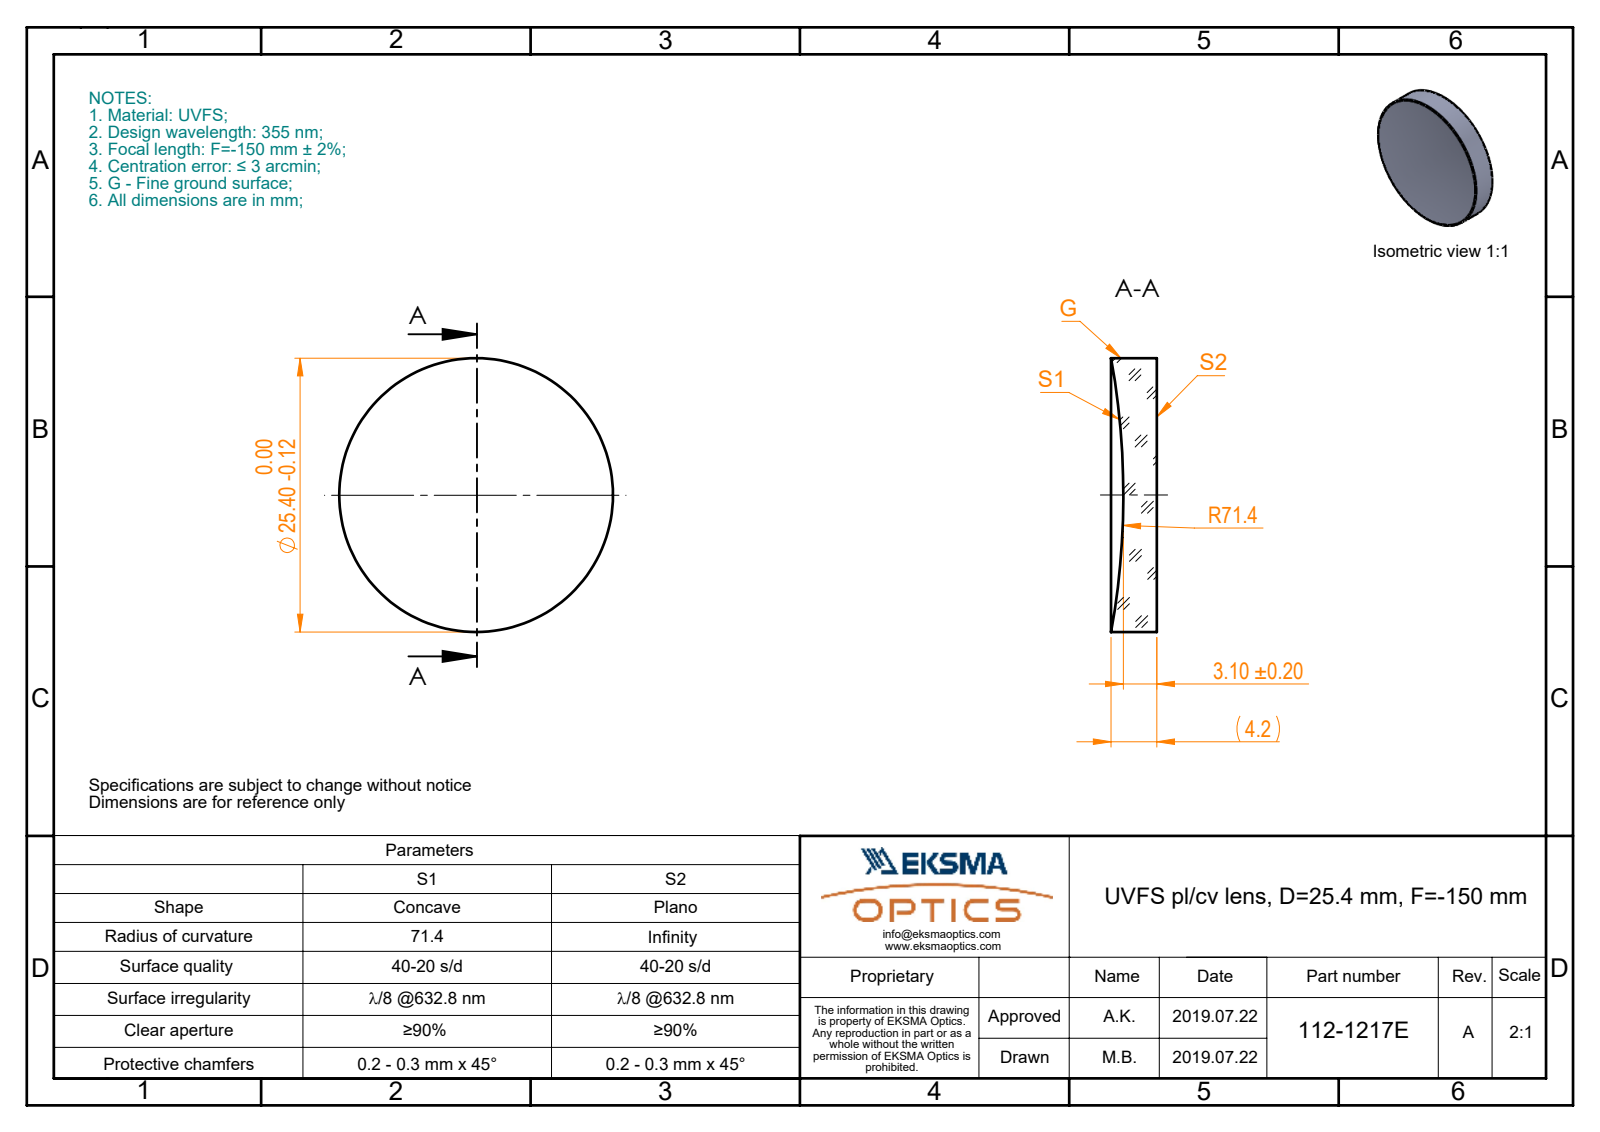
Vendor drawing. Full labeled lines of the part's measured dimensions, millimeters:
Part name (STEP PRODUCT): 112-1217E UVFS pl-cv 25.4 F-150
STEP written by: SolidWorks 2017 (CONFIG_CONTROL_DESIGN)
Units: millimetres
Bodies: 1 solid, 5 faces (1 planar, 2 cylindrical, 2 other)
Overall size (bounding box): 12.7 × 12.7 × 3.04
Volume: 364 mm³ · Surface area: 375 mm²
Round bosses / shafts (diameter × count): ⌀12.7 ×1
